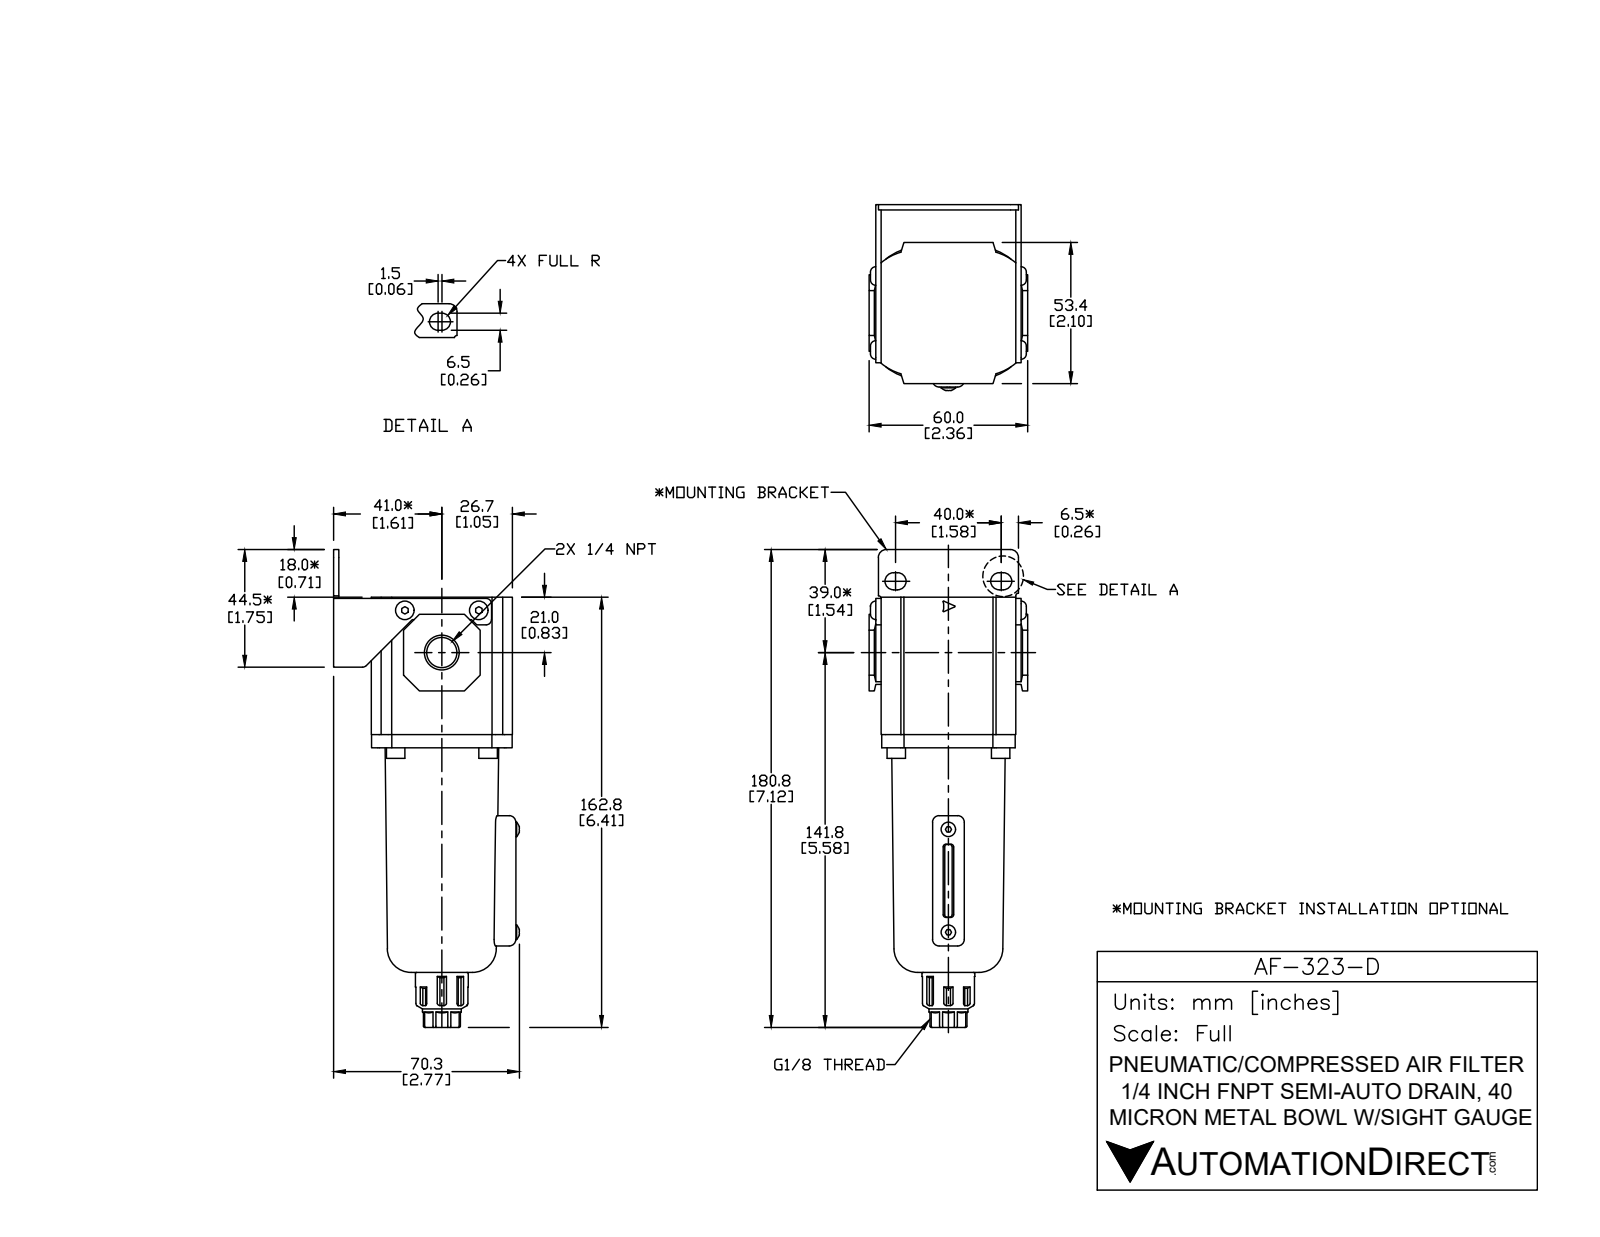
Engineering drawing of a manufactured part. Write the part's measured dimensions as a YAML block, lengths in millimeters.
part_name: "AF-323-D"
step_written_by: "SolidWorks 2015 (CONFIG_CONTROL_DESIGN)"
units: millimeters
bodies: {solids: 9, faces: 416, planar: 245, cylindrical: 98, other: 73}
overall_size: [181.1, 71, 60]
volume: 278043
surface_area: 49410
round_holes:
  - {diameter: 3.4, count: 2}
  - {diameter: 6.2, count: 1}
  - {diameter: 11.13, count: 1}
round_bosses_or_shafts:
  - {diameter: 7, count: 4}
  - {diameter: 5.5, count: 2}
  - {diameter: 20, count: 1}
  - {diameter: 14.7, count: 1}
partial_cylinders:
  - {radius: 1.3, count: 8}
  - {radius: 2.5, count: 8}
  - {radius: 9.5, count: 8}
  - {radius: 0.5, count: 6}
  - {radius: 2, count: 5}
  - {radius: 0.3, count: 4}
  - {radius: 1, count: 4}
  - {radius: 3.25, count: 4}
face_to_face_distances: [2, 52, 51, 53, 53.4, 12.3, 14.3, 67.7, 65.7, 2.5]
hole_center_spacings: [21.06, 21.46, 28]
